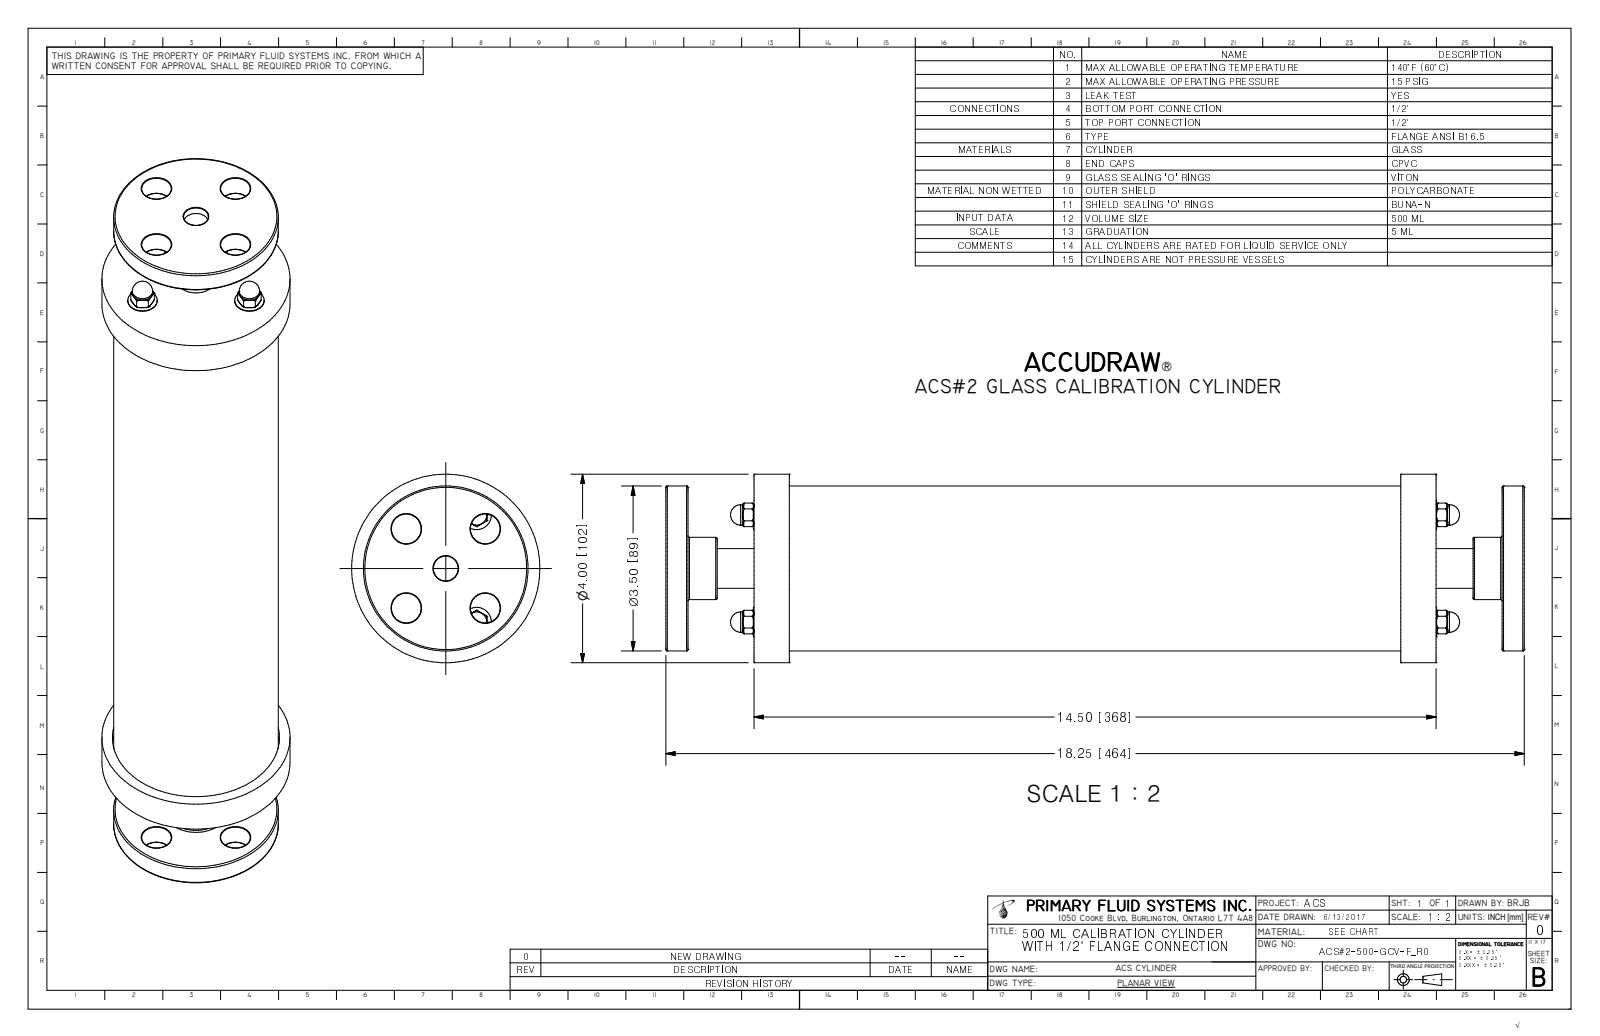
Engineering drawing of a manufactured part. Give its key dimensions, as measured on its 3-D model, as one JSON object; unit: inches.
{"part_name": "ACS#2-500-GCV-F_R0", "step_written_by": "Autodesk Inventor 2009 (AUTOMOTIVE_DESIGN)", "units": "inches", "bodies": {"solids": 1, "faces": 571, "planar": 39, "cylindrical": 123, "other": 409}, "overall_size": [18.25, 4, 4], "volume_in3": 52.92, "surface_area_in2": 626.6, "round_holes": [[0.63, 4], [0.18, 3], [0.266, 3], [0.281, 3], [0.526, 1], [1.811, 1], [2.05, 1], [3.25, 1], [3.55, 1]], "round_bosses_or_shafts": [[0.625, 3], [0.25, 3], [4, 1], [3.5, 1], [3.2, 1], [1.969, 1], [1.7, 1], [1.32, 1]], "face_to_face_distances": [0.75, 13.75, 1.875, 16.375, 2.625, 15.625, 0.47, 17.78, 1.405, 2.155], "hole_center_spacings": [1.188, 1.68, 1.313, 2.273, 0.349, 0.964, 1.525, 1.985]}
